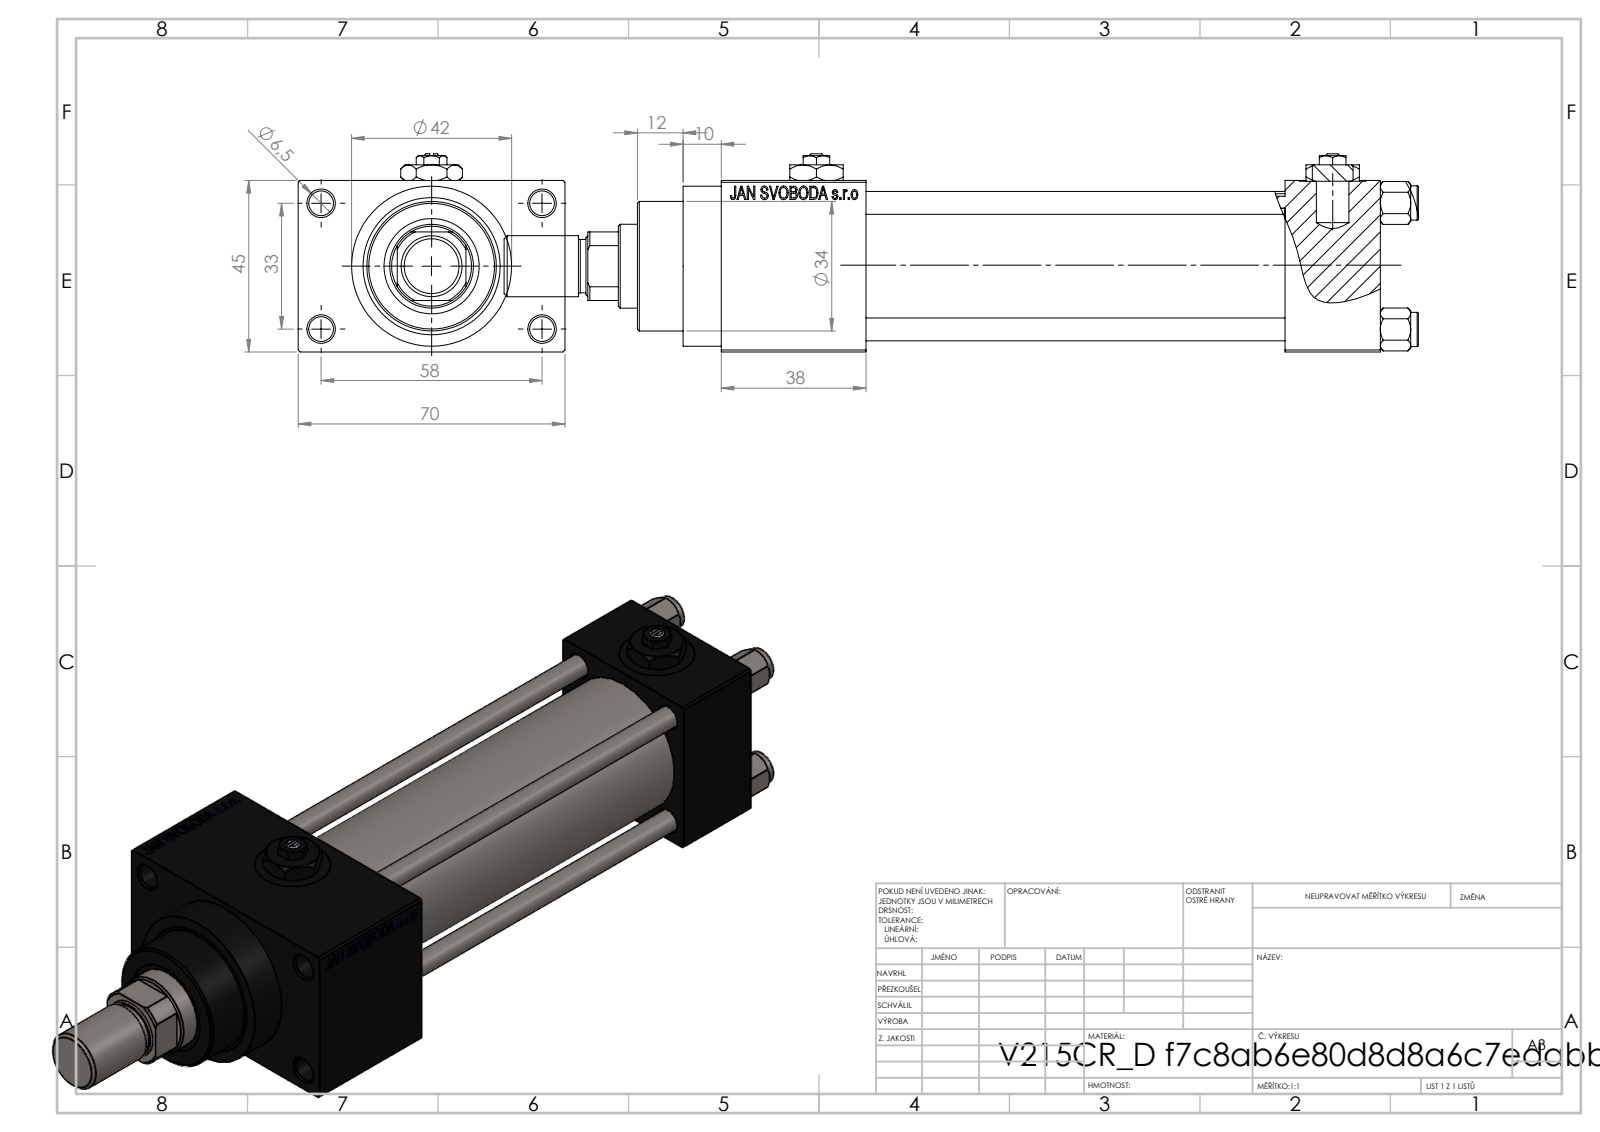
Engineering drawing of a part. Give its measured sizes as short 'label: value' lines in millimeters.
name: V215CR_D_TYCINKA; V215_VC_A; Zatka_pro_OIL_PORT; ROD_END_AH (+3 more)
written by: SolidWorks 2019 (CONFIG_CONTROL_DESIGN)
unit: mm
bodies: 14 solids, 1217 faces (546 planar, 103 cylindrical, 568 other)
size: 240 × 70 × 52
volume: 295 572 mm³; area: 105 178 mm²
holes: 4× ⌀6, 4× ⌀6.5, 4× ⌀13.16, 4× ⌀20, 3× ⌀7, 1× ⌀10.5, 1× ⌀22, 1× ⌀24, 1× ⌀25, 1× ⌀32, 1× ⌀33
bosses: 4× ⌀9, 1× ⌀42, 1× ⌀38, 1× ⌀34, 1× ⌀16, 1× ⌀14
rounds: 1× R10.5
face distances: 45, 25, 12.5, 110, 135, 57.5, 148, 38, 173, 70
hole spacings: 12.4, 23.48, 33.2, 33.37, 35.35, 45.6, 56.35, 33
